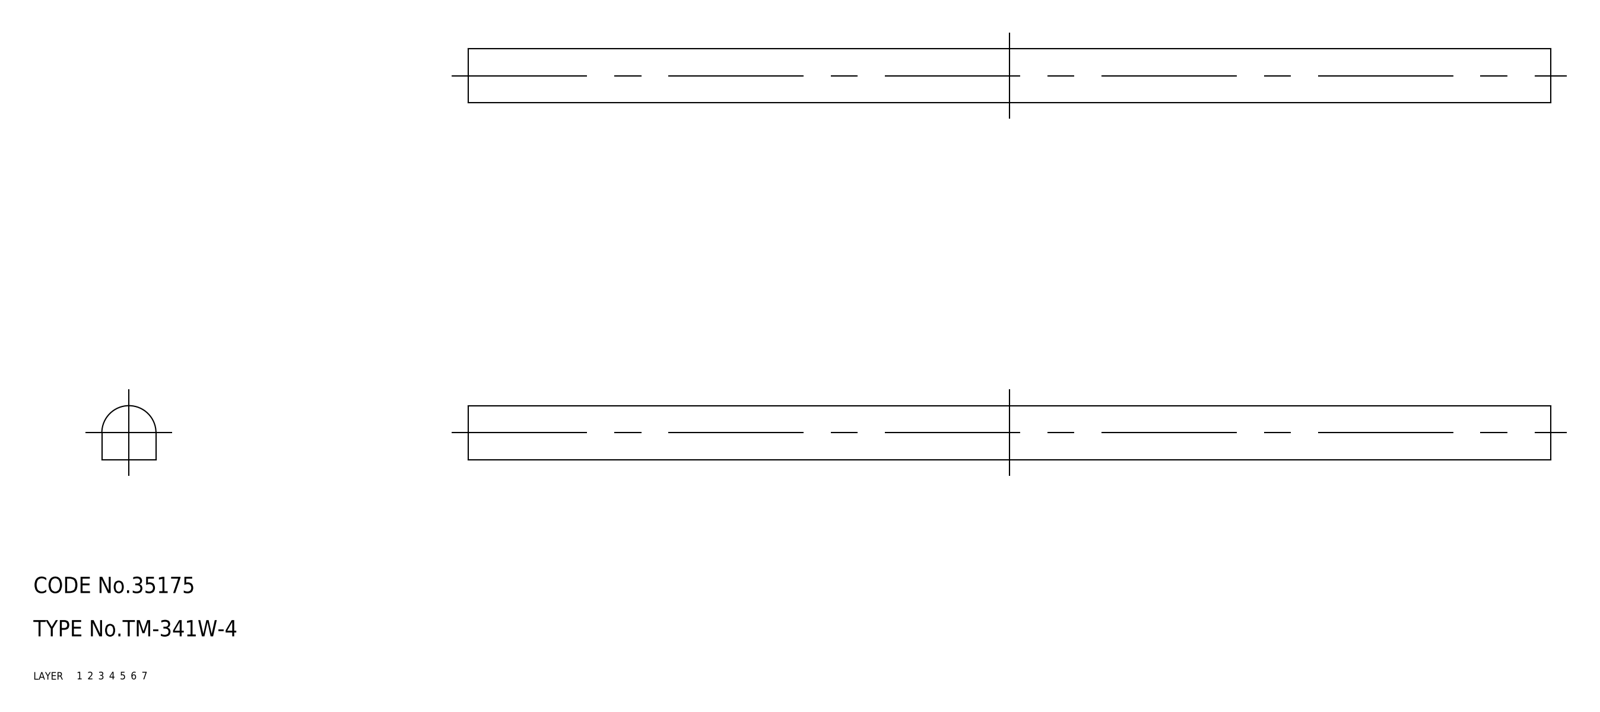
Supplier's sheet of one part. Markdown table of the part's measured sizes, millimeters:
| quantity | value |
| --- | --- |
| part name | rubber foam; TM_341W_4 |
| STEP written by | SolidWorks 2015 (AUTOMOTIVE_DESIGN) |
| units | millimeters |
| bodies | 1 solid, 6 faces (5 planar, 1 cylindrical, 0 other) |
| overall size | 200 × 10 × 10 |
| volume | 17 854 mm³ |
| surface area | 7 320 mm² |
| partial cylindrical surfaces (radius × count) | 5 × 1 |
| main face-to-face distances | 10, 200 |
